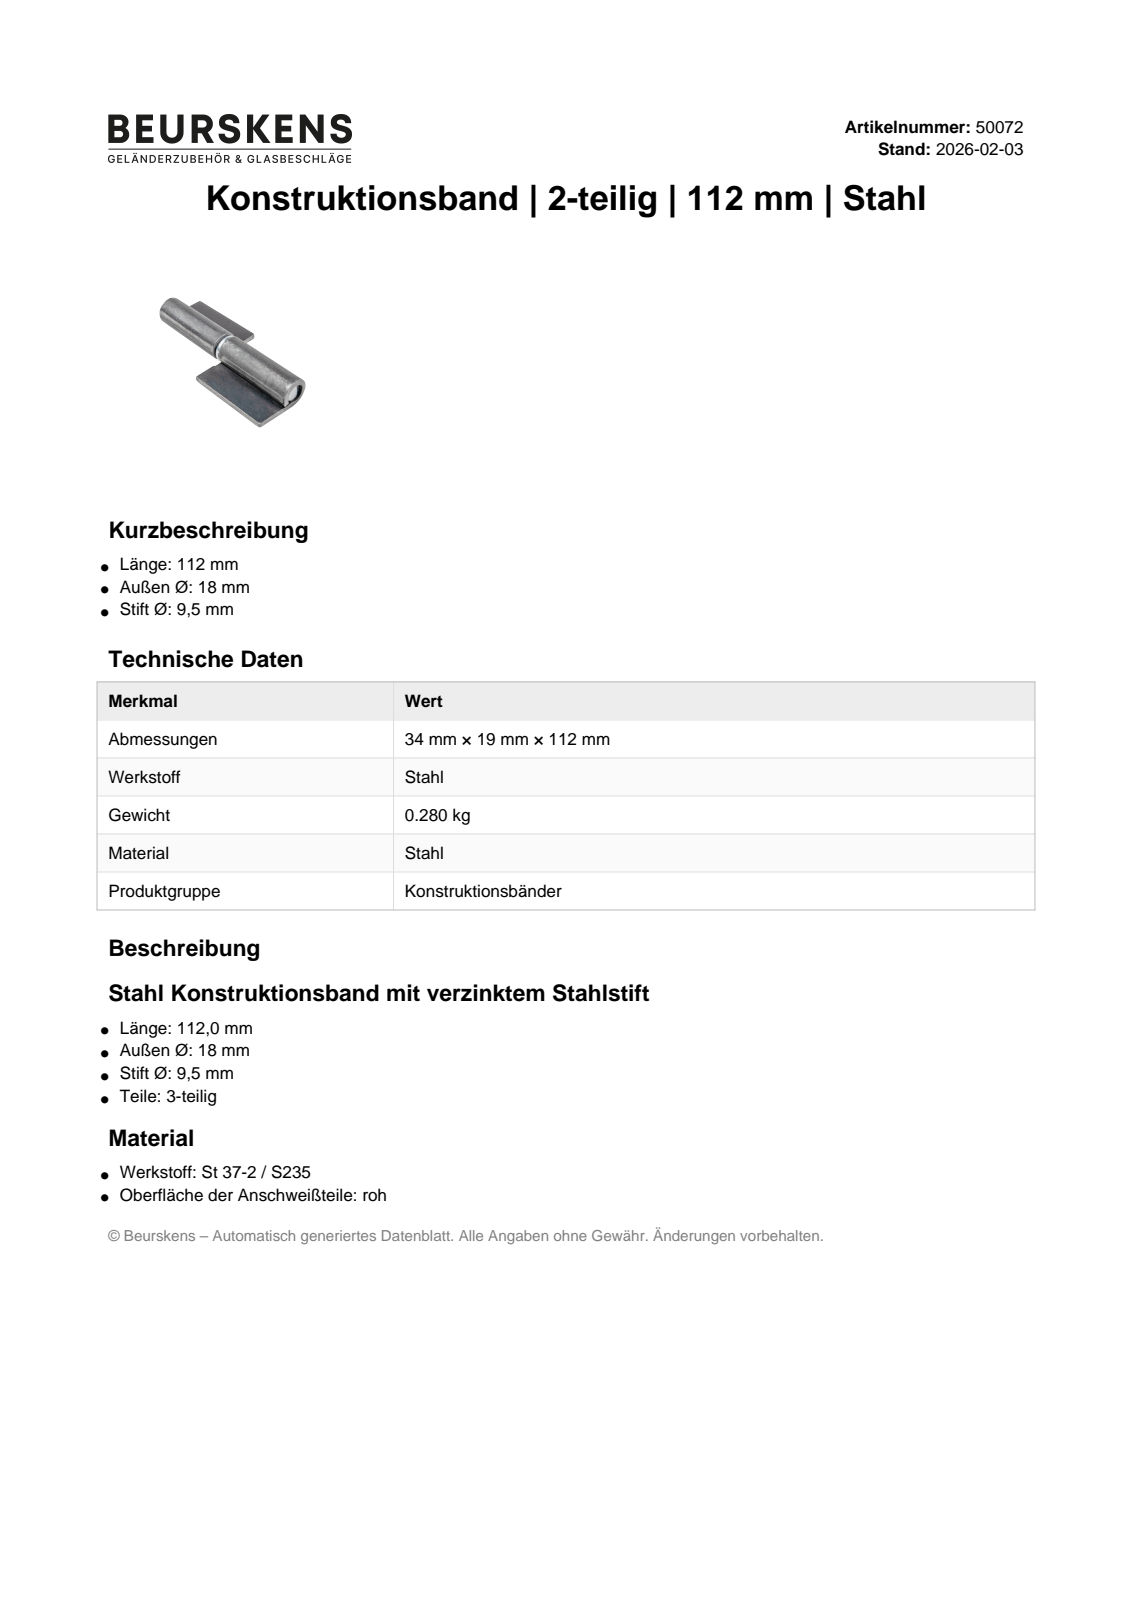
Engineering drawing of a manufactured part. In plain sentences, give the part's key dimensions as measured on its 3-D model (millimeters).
The part is named "50072; 50072 Stift; 50072 Lasche". Its 3-D file was written by "Autodesk Inventor 2023 (AUTOMOTIVE_DESIGN)". It is 3 solids with 25 faces: 16 planar, 6 cylindrical and 3 other. Overall it measures 112 by 45.3 by 29.48 millimeters. Its volume is 36 102 cubic millimeters and its surface area 19 277 square millimeters. Round holes: 1 of diameter 10.2. Round bosses or shafts: 1 of diameter 18.2, 1 of diameter 10. The main face-to-face distances are 4, 54, 57, 3, 111, 49.99, 0.5, 54.5, 57.5, 111.5.
